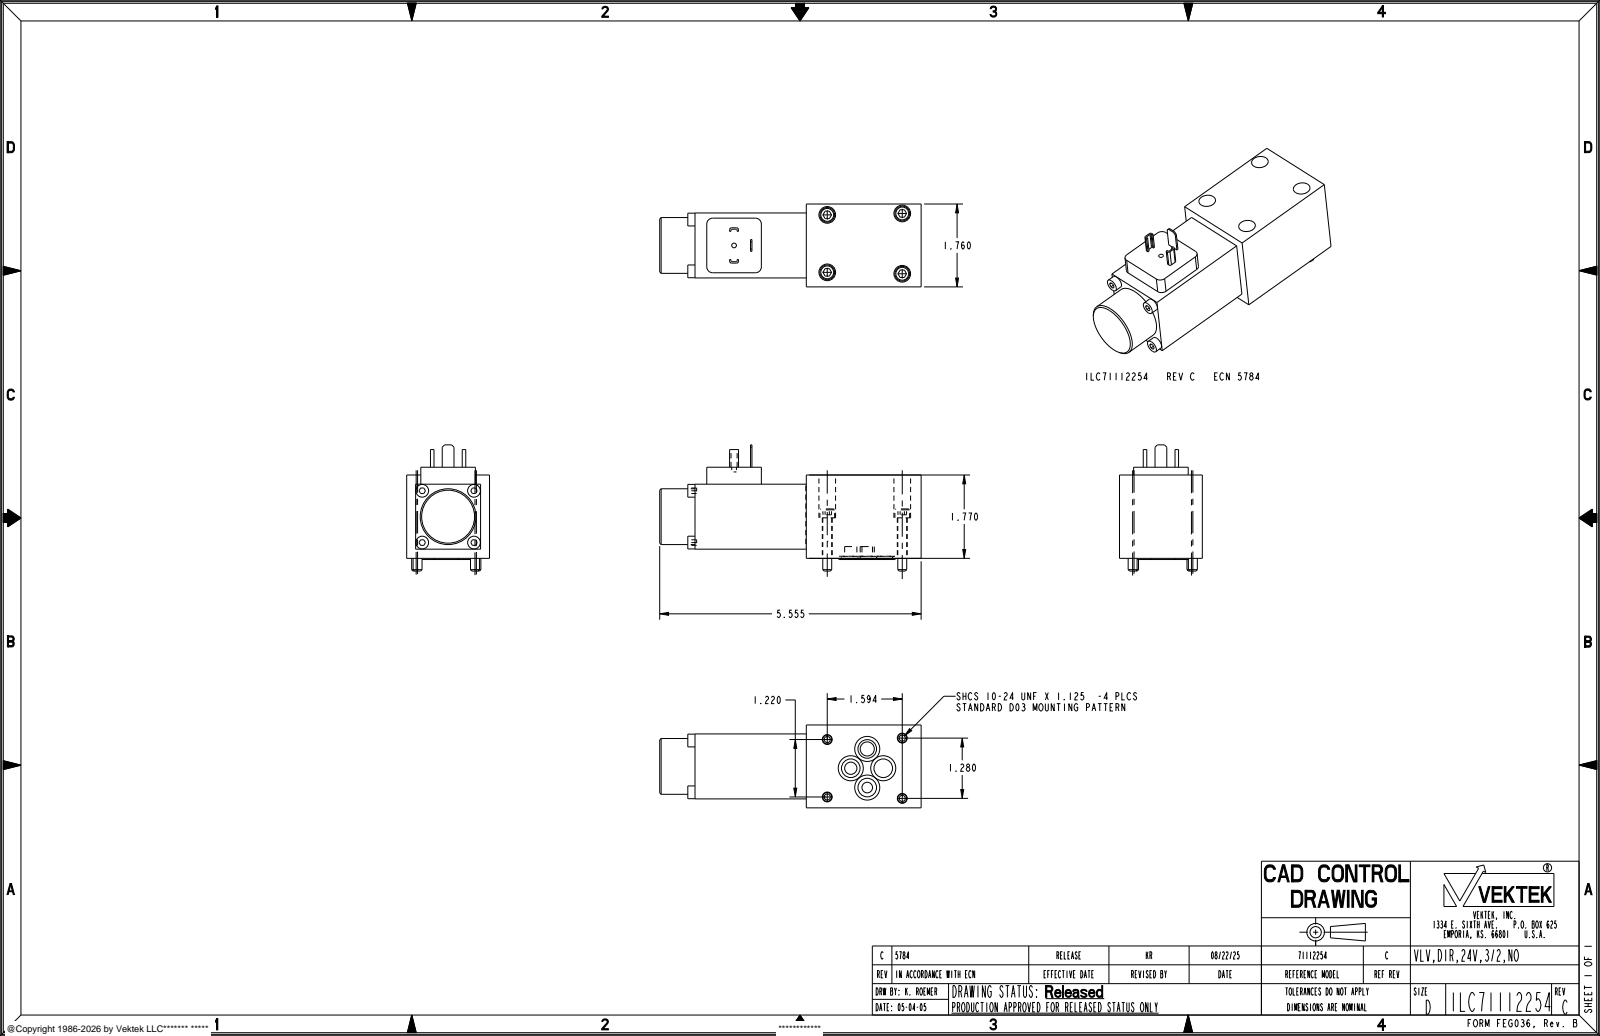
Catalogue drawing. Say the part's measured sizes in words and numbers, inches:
The part is named "ILC71112254". Its 3-D file was written by "CREO PARAMETRIC BY PTC INC, 2021164 (AUTOMOTIVE_DESIGN)". It is 1 solid with 234 faces: 130 planar, 78 cylindrical and 26 other. Overall it measures 5.555 by 2.68 by 1.76 inches. Its volume is 13.04 cubic inches and its surface area 54.95 square inches. Round holes: 4 of diameter 0.21, 4 of diameter 0.354, 4 of diameter 0.49, 1 of diameter 0.1, 1 of diameter 0.225, 1 of diameter 0.26, 1 of diameter 0.3, 1 of diameter 0.45, 1 of diameter 1.315. Round bosses or shafts: 4 of diameter 0.313, 4 of diameter 0.271, 4 of diameter 0.19, 1 of diameter 1.265, 1 of diameter 1.185, 1 of diameter 0.15. Partial cylindrical surfaces (rounded edges, fillets, slot ends): 4 of radius 0.015, 4 of radius 0.04, 4 of radius 0.125. The main face-to-face distances are 0.19, 1.57, 0.195, 1.575, 1.38, 1.76, 1.77, 2.44, 0.165, 0.36. The hole center spacings are 0.533, 0.539, 0.757, 0.779, 0.788, 0.873, 1.268, 1.287.
